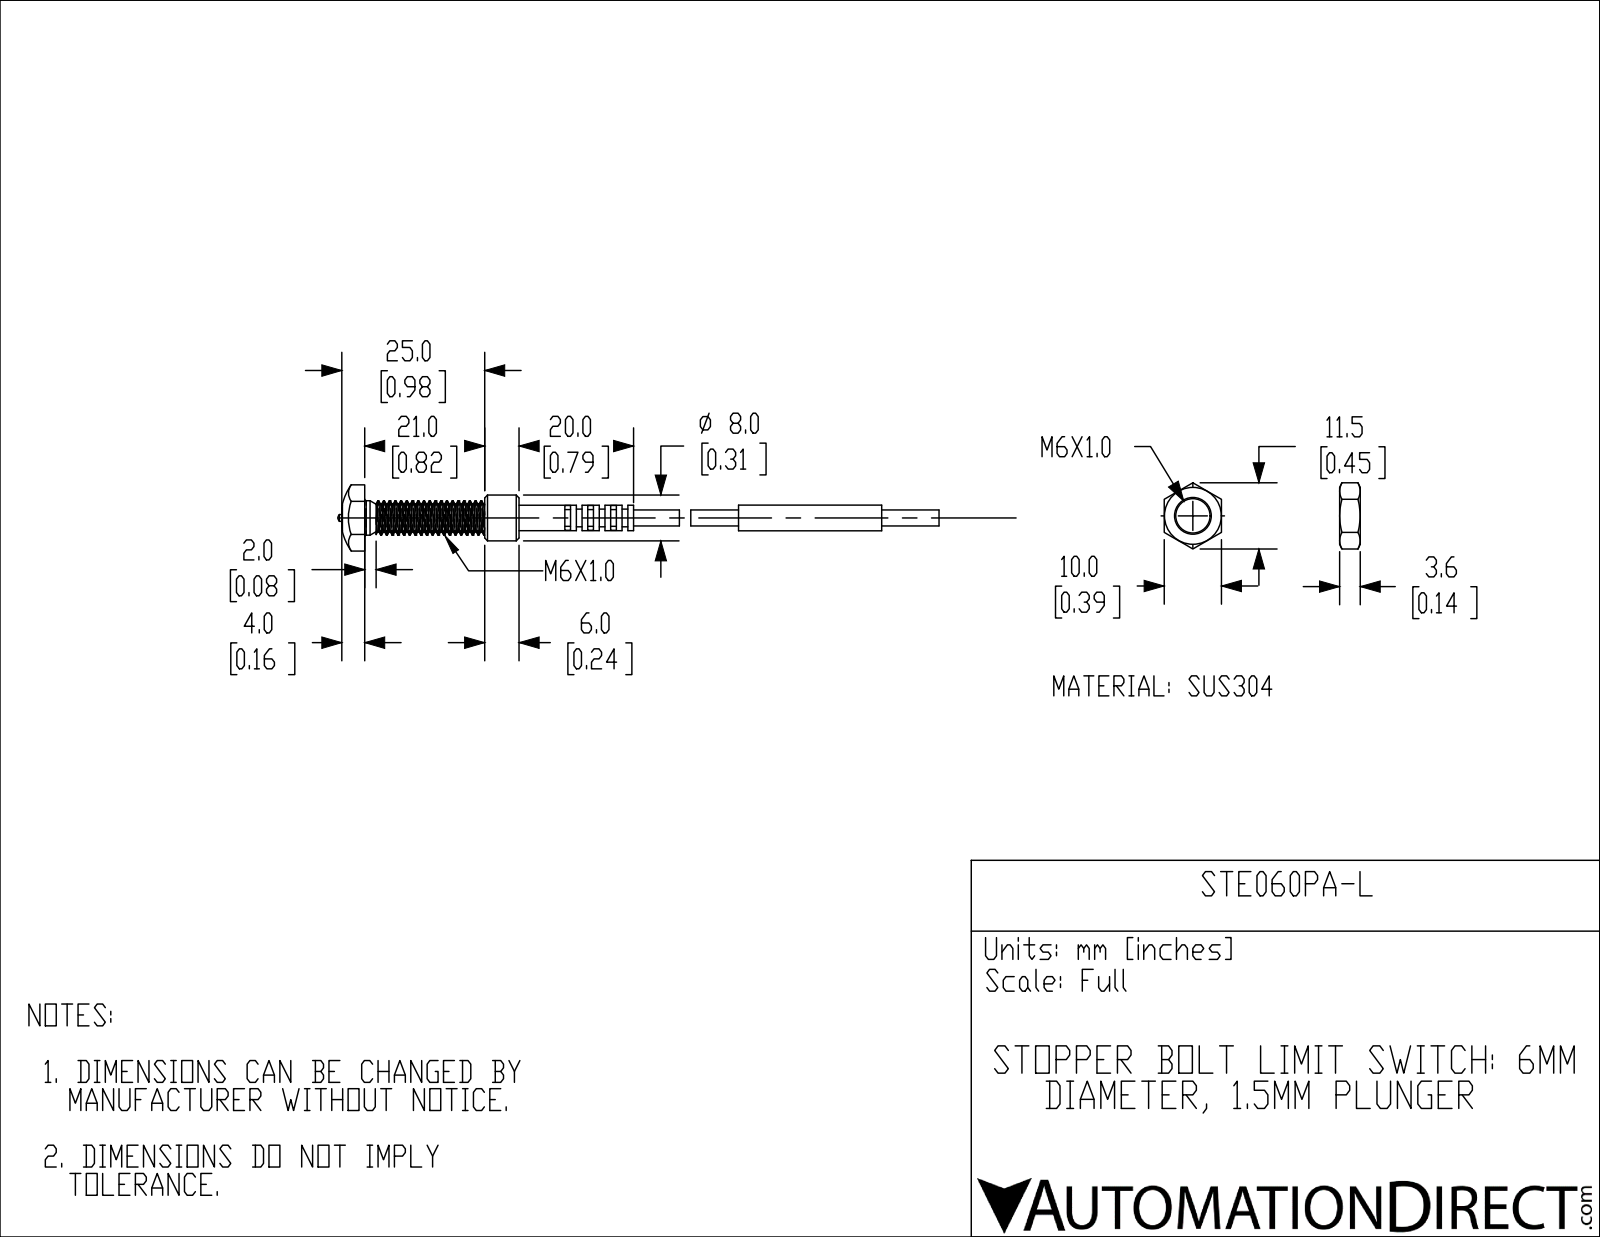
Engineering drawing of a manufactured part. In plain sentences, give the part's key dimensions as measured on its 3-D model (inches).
The part is named "STE060PA-L". Its 3-D file was written by "SolidWorks 2018 (AUTOMOTIVE_DESIGN)". It is 2 solids with 77 faces: 48 planar, 21 cylindrical and 8 other. Overall it measures 4.134 by 0.455 by 0.394 inches. Its volume is 0.123 cubic inches and its surface area 2.826 square inches. Round bosses or shafts: 1 of diameter 0.315, 1 of diameter 0.236, 1 of diameter 0.177, 1 of diameter 0.175, 1 of diameter 0.122, 1 of diameter 0.11, 1 of diameter 0.047. The main face-to-face distances are 0.039, 0.394, 0.079, 0.157, 0.118, 0.236, 0.197, 0.315, 0.276, 0.354.
